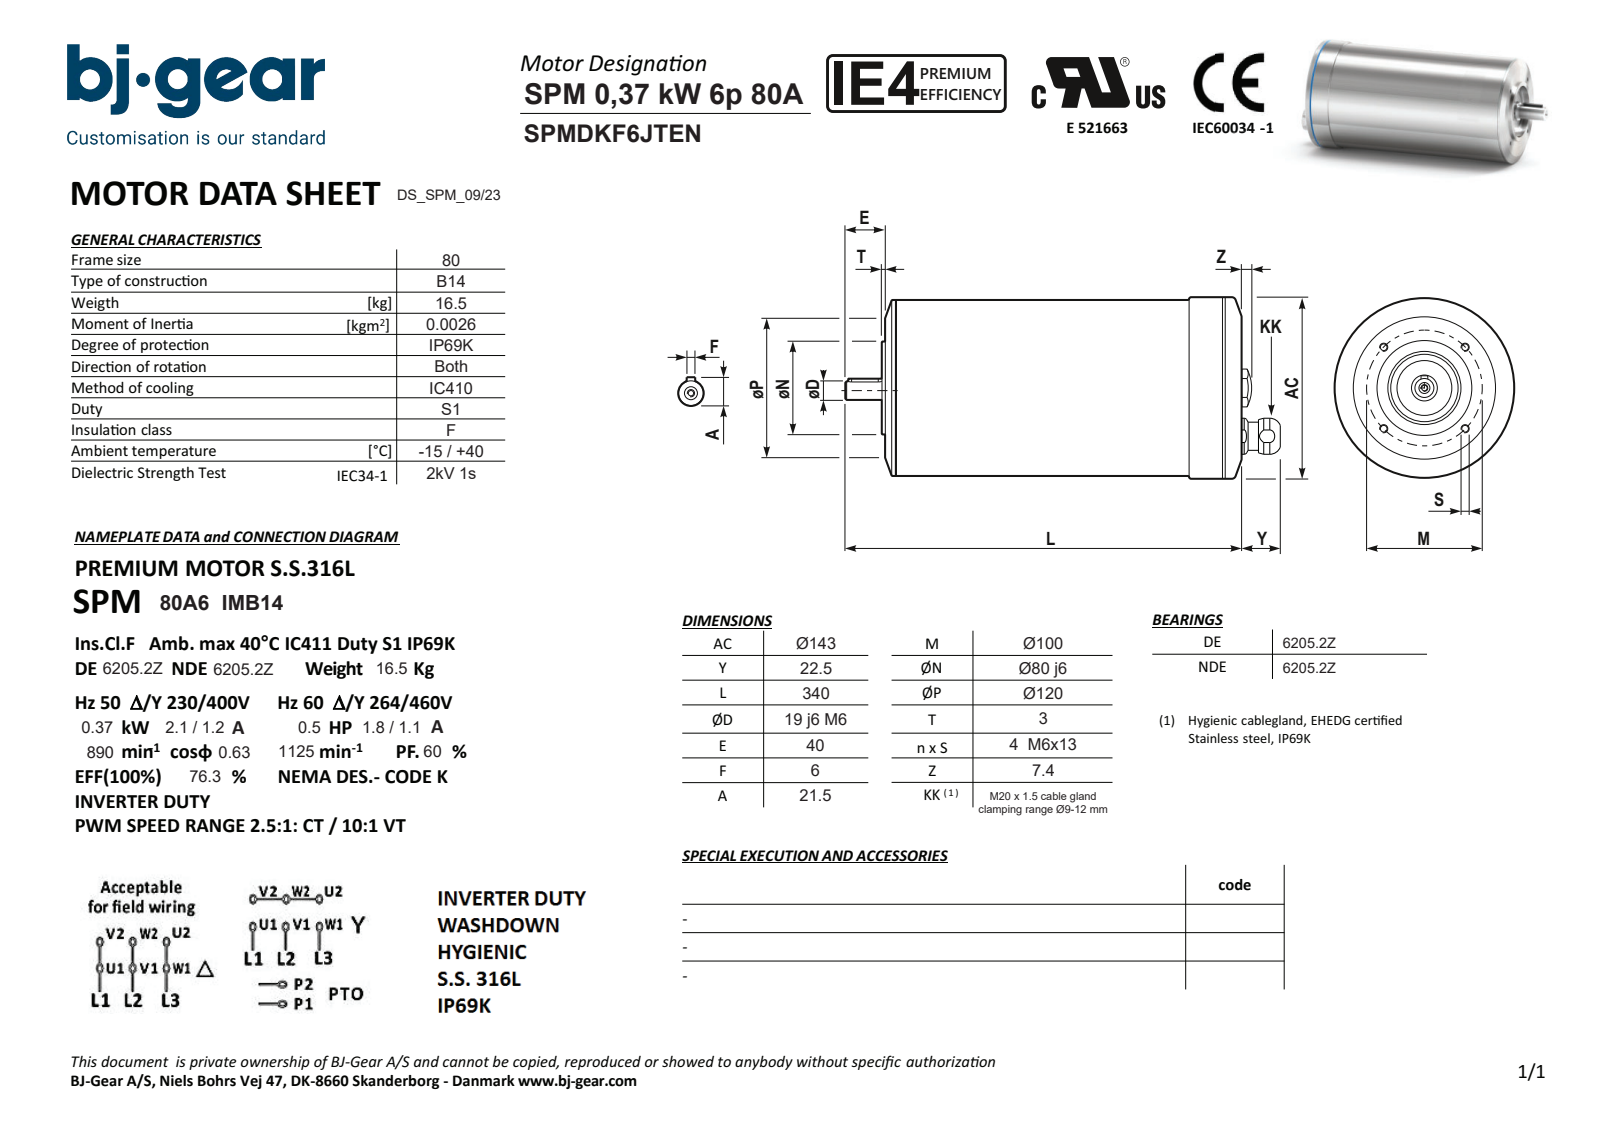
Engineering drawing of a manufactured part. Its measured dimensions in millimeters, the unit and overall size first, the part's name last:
Units: millimetres
Overall size (bounding box): 367.5 × 143 × 143
Round holes (diameter × count): ⌀4.92 ×5, ⌀6.4 ×1, ⌀7 ×1, ⌀13.4 ×1, ⌀68 ×1
Round bosses / shafts (diameter × count): ⌀143 ×1, ⌀142.98 ×1, ⌀139 ×1, ⌀138.98 ×1, ⌀80 ×1, ⌀25 ×1, ⌀20 ×1, ⌀19 ×1
Partial cylindrical surfaces — rounded edges, fillets, slot ends (radius × count): R3 ×2, R12.8 ×1
Main face-to-face distances: 300, 6, 294, 9, 303, 3, 24, 340, 46, 40
Hole centre spacings: 50.01, 70.72, 35.46, 81.44, 100.01, 38
Volume: 4 570 000 mm³ · Surface area: 168 444 mm²
Bodies: 1 solid, 87 faces (30 planar, 32 cylindrical, 25 other)
Part name (STEP PRODUCT): SPMDKF6JTENN4KSA1-N---NNN
STEP written by: Solid Edge (AUTOMOTIVE_DESIGN)
